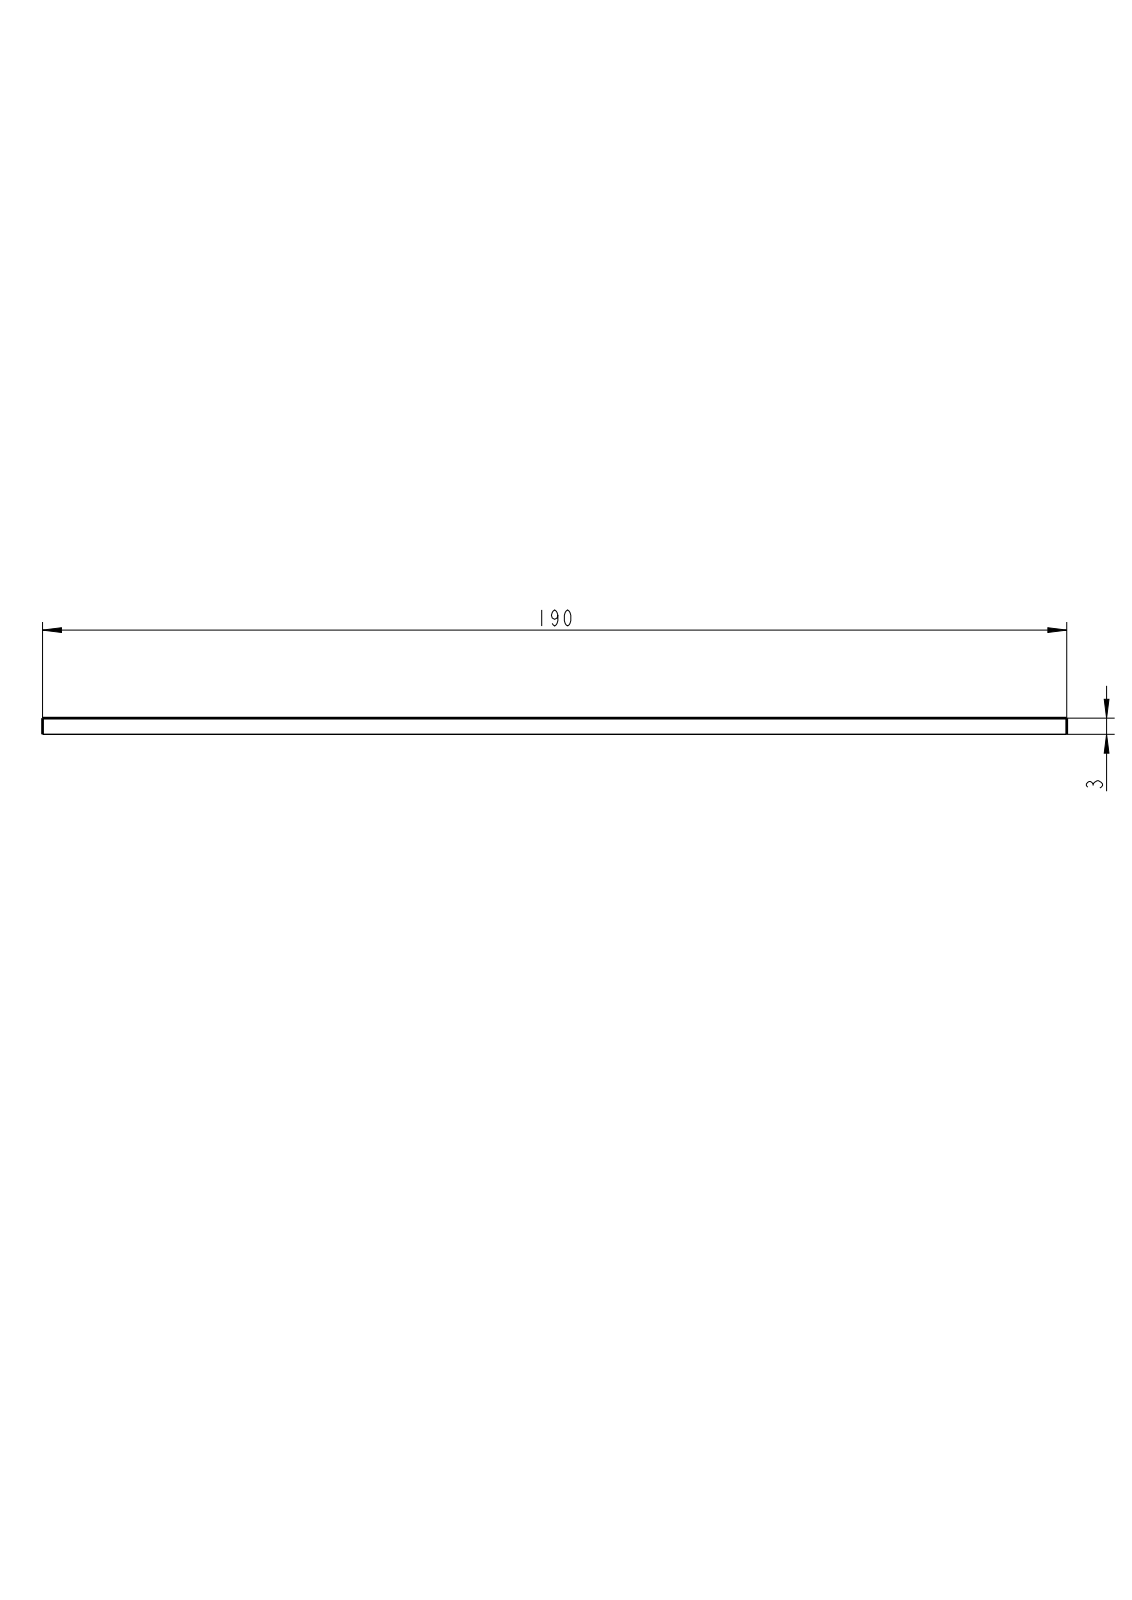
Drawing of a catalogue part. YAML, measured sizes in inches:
part_name: "T-01185; BKG2002BL2_ASM"
step_written_by: "CREO PARAMETRIC BY PTC INC, 2022024 (AUTOMOTIVE_DESIGN)"
units: inches
bodies: {solids: 1, faces: 6, planar: 6, cylindrical: 0, other: 0}
overall_size: [39.331, 7.48, 0.118]
volume: 34.75
surface_area: 599.5
face_to_face_distances: [0.118, 7.48, 39.331]
